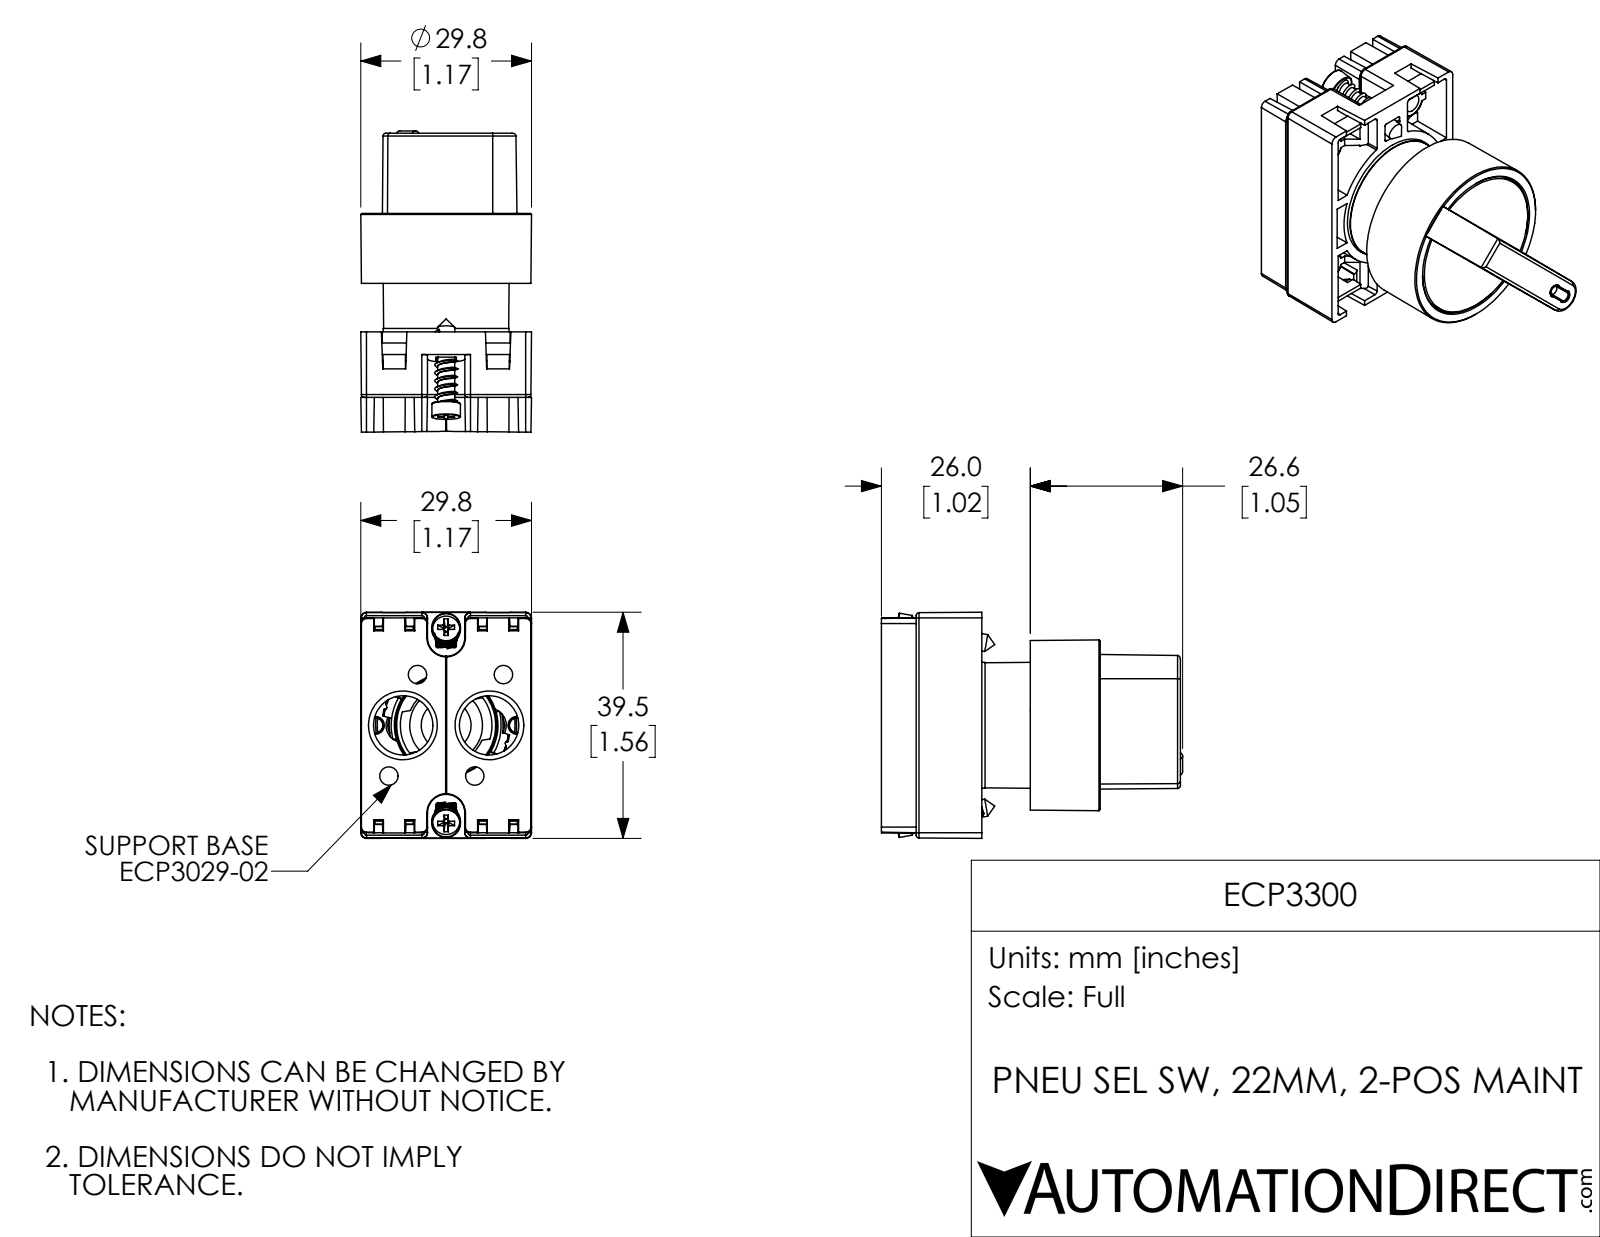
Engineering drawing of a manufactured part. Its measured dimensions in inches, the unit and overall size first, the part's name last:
Units: inches
Overall size (bounding box): 2.071 × 1.555 × 1.173
Round holes (diameter × count): ⌀0.081 ×4, ⌀0.407 ×2, ⌀0.5 ×1, ⌀0.551 ×1, ⌀0.697 ×1, ⌀0.75 ×1, ⌀0.756 ×1, ⌀0.854 ×1, ⌀0.976 ×1, ⌀1.024 ×1
Round bosses / shafts (diameter × count): ⌀0.197 ×2, ⌀0.118 ×2, ⌀1.004 ×1, ⌀0.866 ×1, ⌀0.85 ×1, ⌀0.669 ×1, ⌀0.343 ×1
Partial cylindrical surfaces — rounded edges, fillets, slot ends (radius × count): R0.02 ×21, R0.012 ×10, R0.039 ×9, R0.006 ×8, R0.008 ×4, R0.008 ×2, R0.118 ×2, R0.128 ×2
Main face-to-face distances: 1.265, 0.059, 0.067, 0.299, 0.715, 0.814, 0.451, 0.587, 0.743, 0.966
Hole centre spacings: 0.304, 0.541, 0.817, 0.295, 0.472, 0.972, 1.081, 0.591
Volume: 1.095 in³ · Surface area: 31.53 in²
Bodies: 8 solids, 839 faces (404 planar, 157 cylindrical, 278 other)
Part name (STEP PRODUCT): ECP3300
STEP written by: SolidWorks 2021 (CONFIG_CONTROL_DESIGN)
